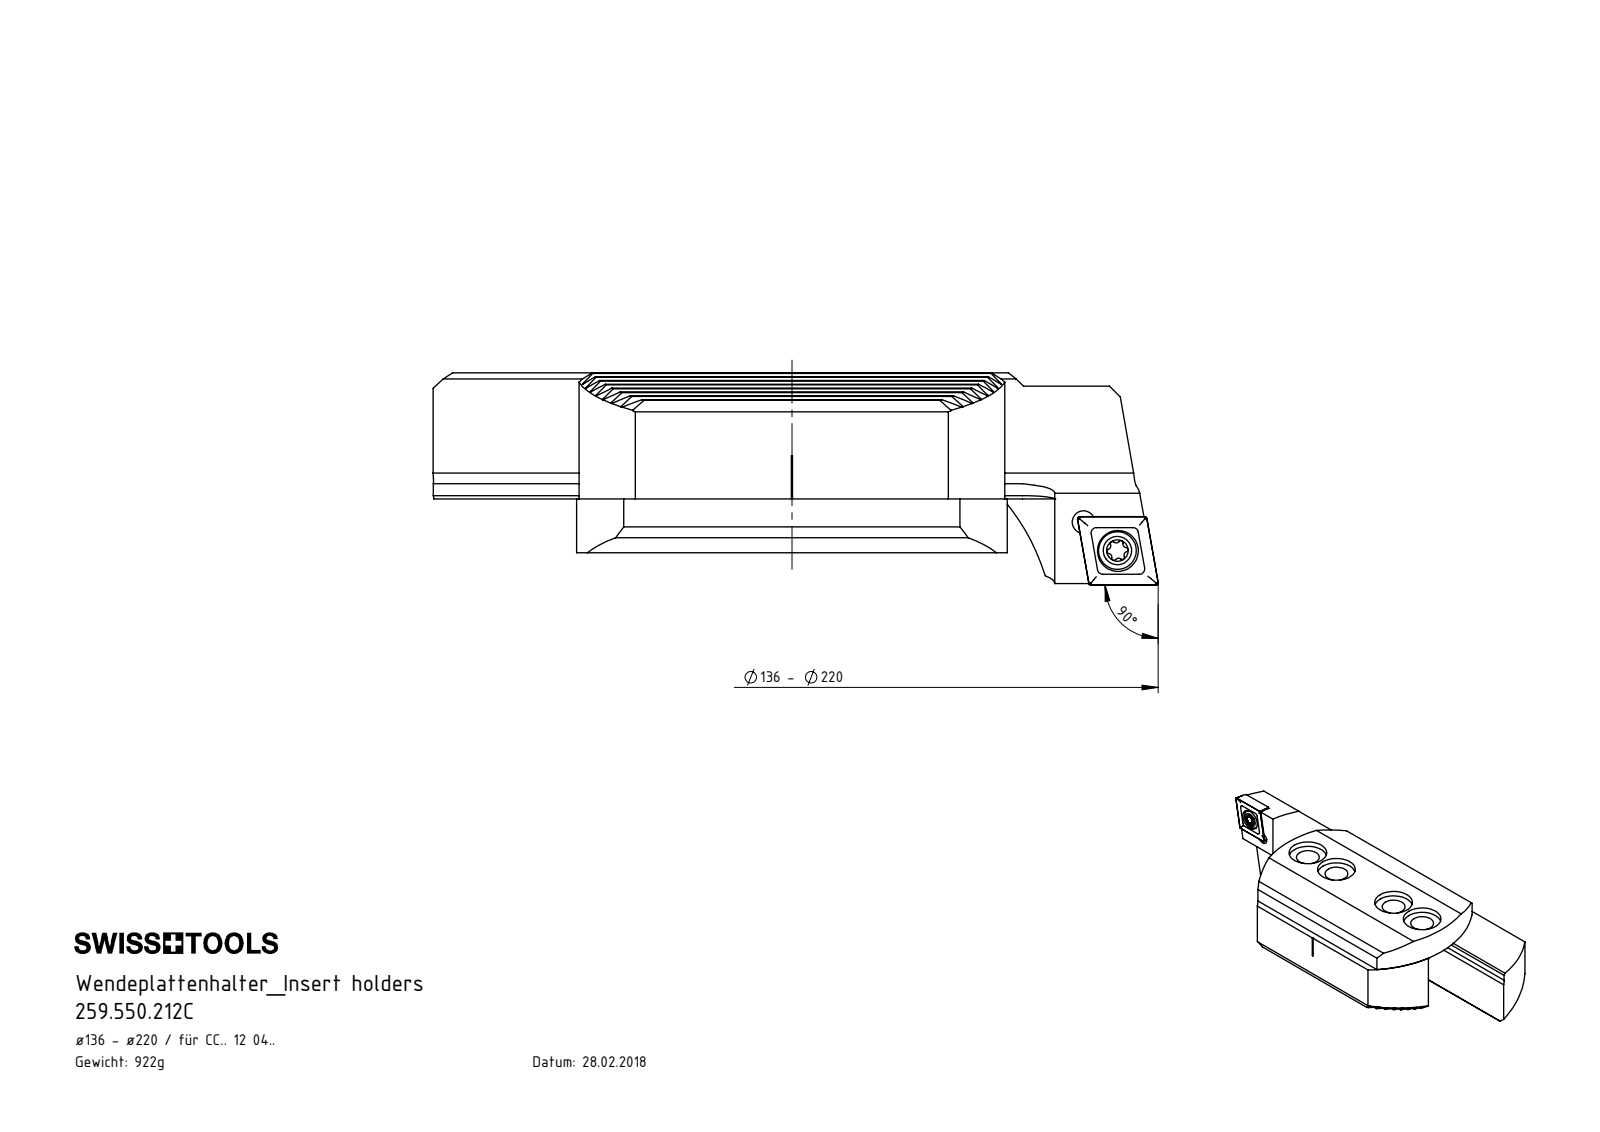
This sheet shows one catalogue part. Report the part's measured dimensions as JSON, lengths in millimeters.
{"part_name": "F00-WCB.136.002_A; F00-WCB.136.003_A; 259.550.212C; F00-WCC.136.001 (+3 more)", "step_written_by": "SolidWorks 2017 (CONFIG_CONTROL_DESIGN)", "units": "millimeters", "bodies": {"solids": 5, "faces": 632, "planar": 382, "cylindrical": 68, "other": 182}, "overall_size": [134.59, 55, 39.4], "volume_mm3": 117488, "surface_area_mm2": 32184, "round_holes": [[8.5, 4], [14, 4], [4.2, 2], [5.5, 1], [7.6, 1]], "round_bosses_or_shafts": [[7, 1], [5, 1]], "partial_cylinders_radius": [[0.2, 16], [0.39, 6], [40, 6], [0.69, 4], [0.69, 2], [0.8, 1], [6, 1]], "face_to_face_distances": [2.38, 4.76, 21.3, 33.7, 7.14, 12.4, 9.52, 10, 4.77, 7.15], "hole_center_spacings": [15, 45, 8.21, 8.33, 30, 60]}
